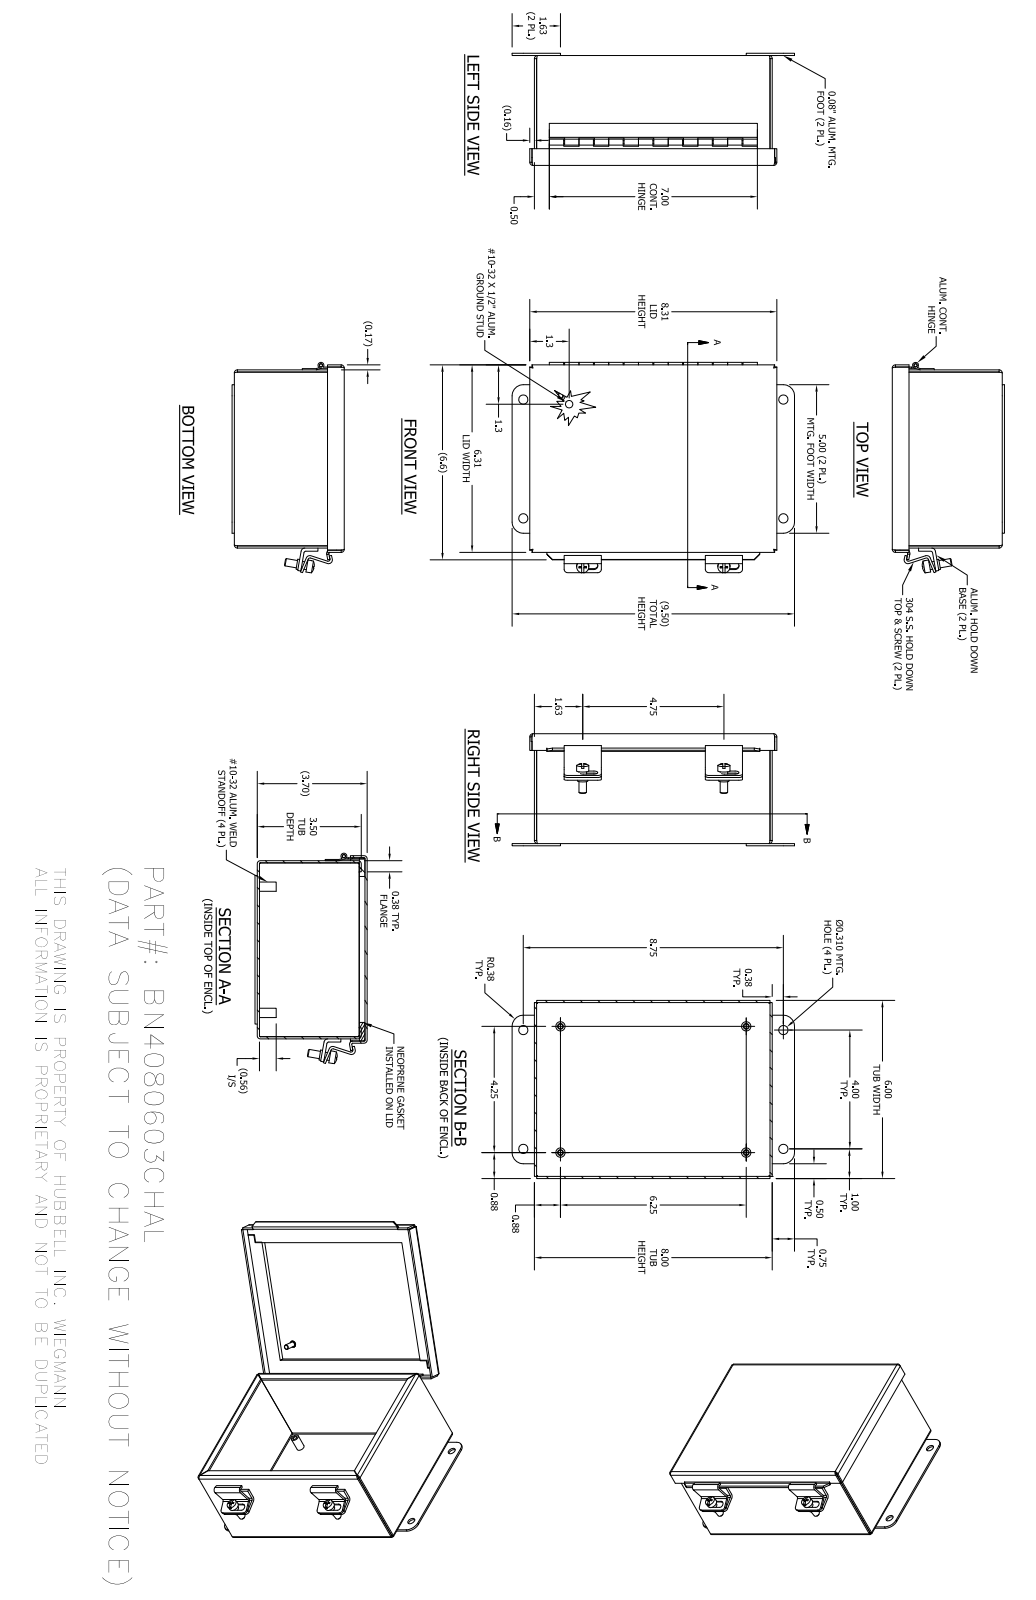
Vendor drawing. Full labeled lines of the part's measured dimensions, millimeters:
Part name (STEP PRODUCT): B_080603_ALBKP; 32841TH; 32841LH; 32841P (+8 more)
STEP written by: Autodesk Inventor 2016 (AUTOMOTIVE_DESIGN)
Units: millimetres
Bodies: 20 solids, 403 faces (249 planar, 113 cylindrical, 41 other)
Overall size (bounding box): 241.3 × 179.98 × 95.86
Volume: 353 757 mm³ · Surface area: 363 144 mm²
Round holes (diameter × count): ⌀3.97 ×4, ⌀6.35 ×4, ⌀7.87 ×4, ⌀4.98 ×2, ⌀2.96 ×1
Round bosses / shafts (diameter × count): ⌀6.35 ×7, ⌀7.95 ×4, ⌀10.4 ×2, ⌀8.74 ×2, ⌀5.08 ×1, ⌀4.83 ×1, ⌀2.54 ×1
Partial cylindrical surfaces — rounded edges, fillets, slot ends (radius × count): R0.79 ×13, R2.67 ×13, R3.17 ×8, R3.38 ×4, R9.53 ×4, R1.6 ×3, R3.2 ×3
Main face-to-face distances: 1.88, 92.08, 92.07, 150.52, 93.95, 1.87, 90.2, 201.32, 152.4, 148.64
Hole centre spacings: 31.91, 109.48, 158.75, 190.53, 217.41, 191.98, 107.95, 101.6
